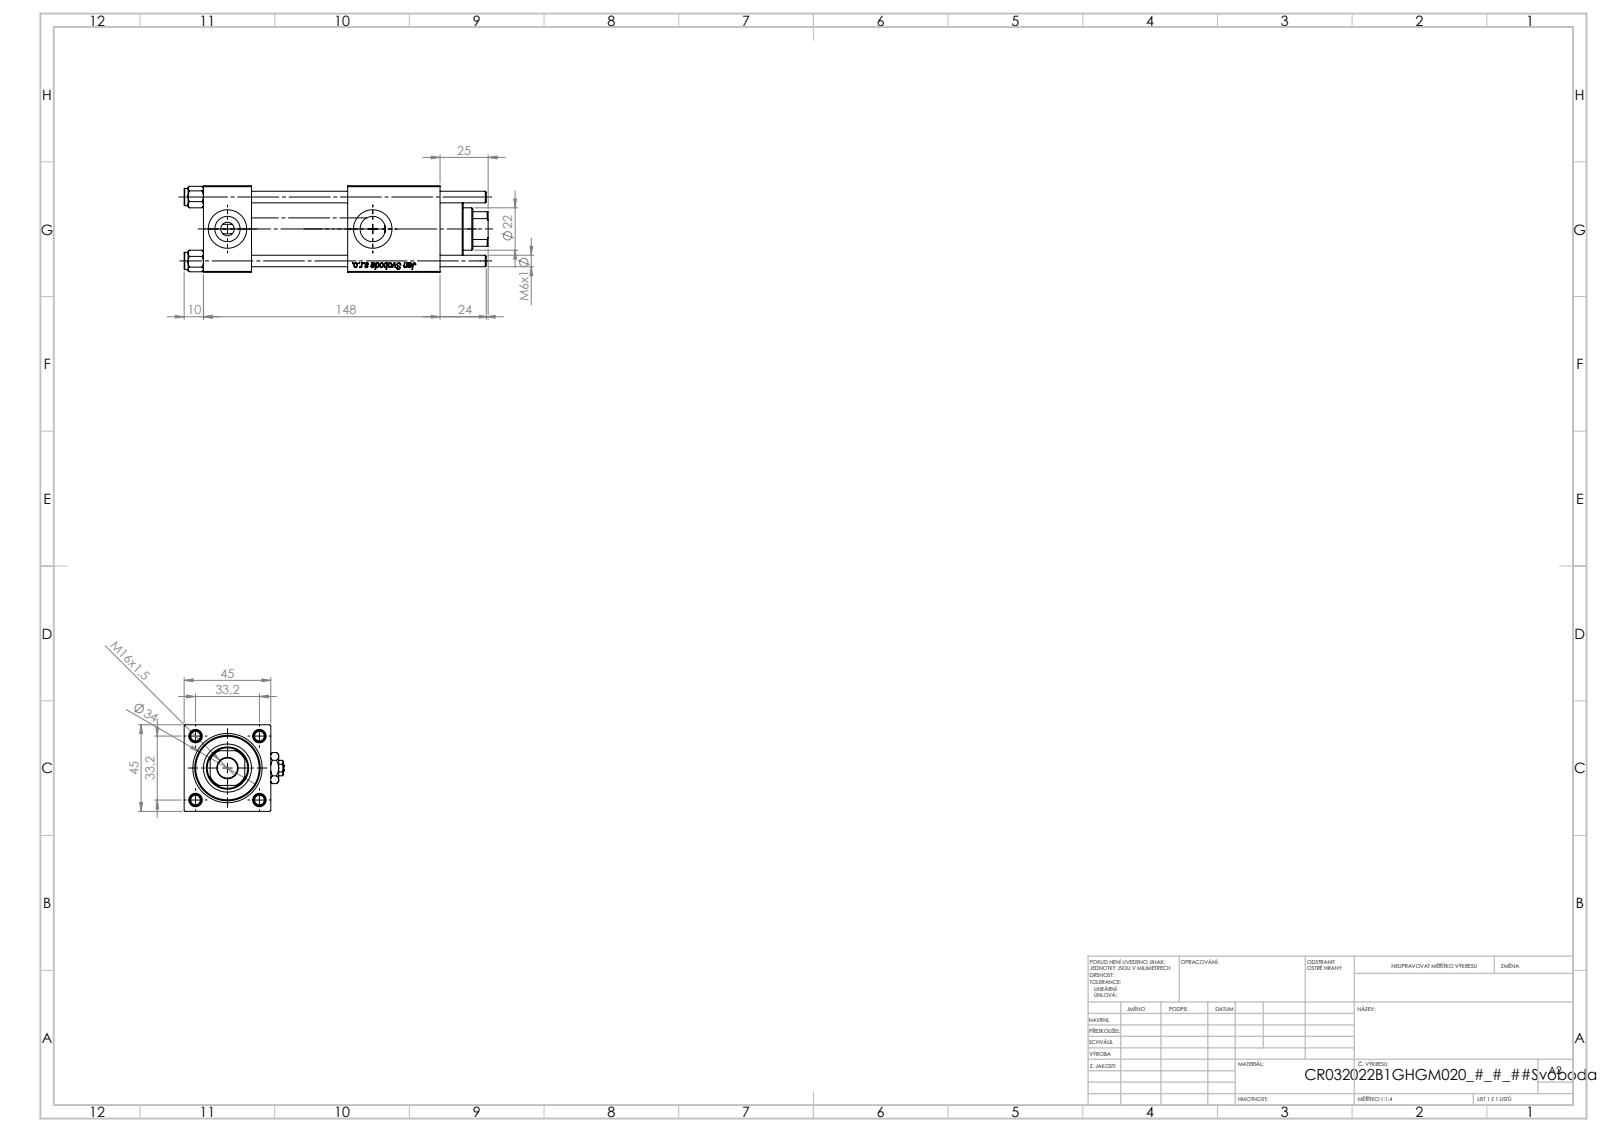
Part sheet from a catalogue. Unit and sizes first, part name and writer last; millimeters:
Units: millimetres
Overall size (bounding box): 158 × 52 × 45
Round holes (diameter × count): ⌀6 ×4, ⌀7 ×2, ⌀13.16 ×2, ⌀20 ×2, ⌀10.5 ×1, ⌀22 ×1, ⌀24 ×1, ⌀25 ×1, ⌀32 ×1, ⌀33 ×1
Round bosses / shafts (diameter × count): ⌀9 ×4, ⌀38 ×1, ⌀34 ×1
Partial cylindrical surfaces — rounded edges, fillets, slot ends (radius × count): R10.5 ×1
Main face-to-face distances: 45, 25, 50, 123, 75, 98, 48, 94.3, 69.3, 19.3
Hole centre spacings: 23.48, 33.2, 46.95, 75.5
Volume: 213 630 mm³ · Surface area: 77 550 mm²
Bodies: 12 solids, 1205 faces (455 planar, 82 cylindrical, 668 other)
Part name (STEP PRODUCT): NUT_M5_B; V215CR_VCP_B; V215CR_B_TYCINKA; Zatka_pro_OIL_PORT (+2 more)
STEP written by: SolidWorks 2019 (CONFIG_CONTROL_DESIGN)
